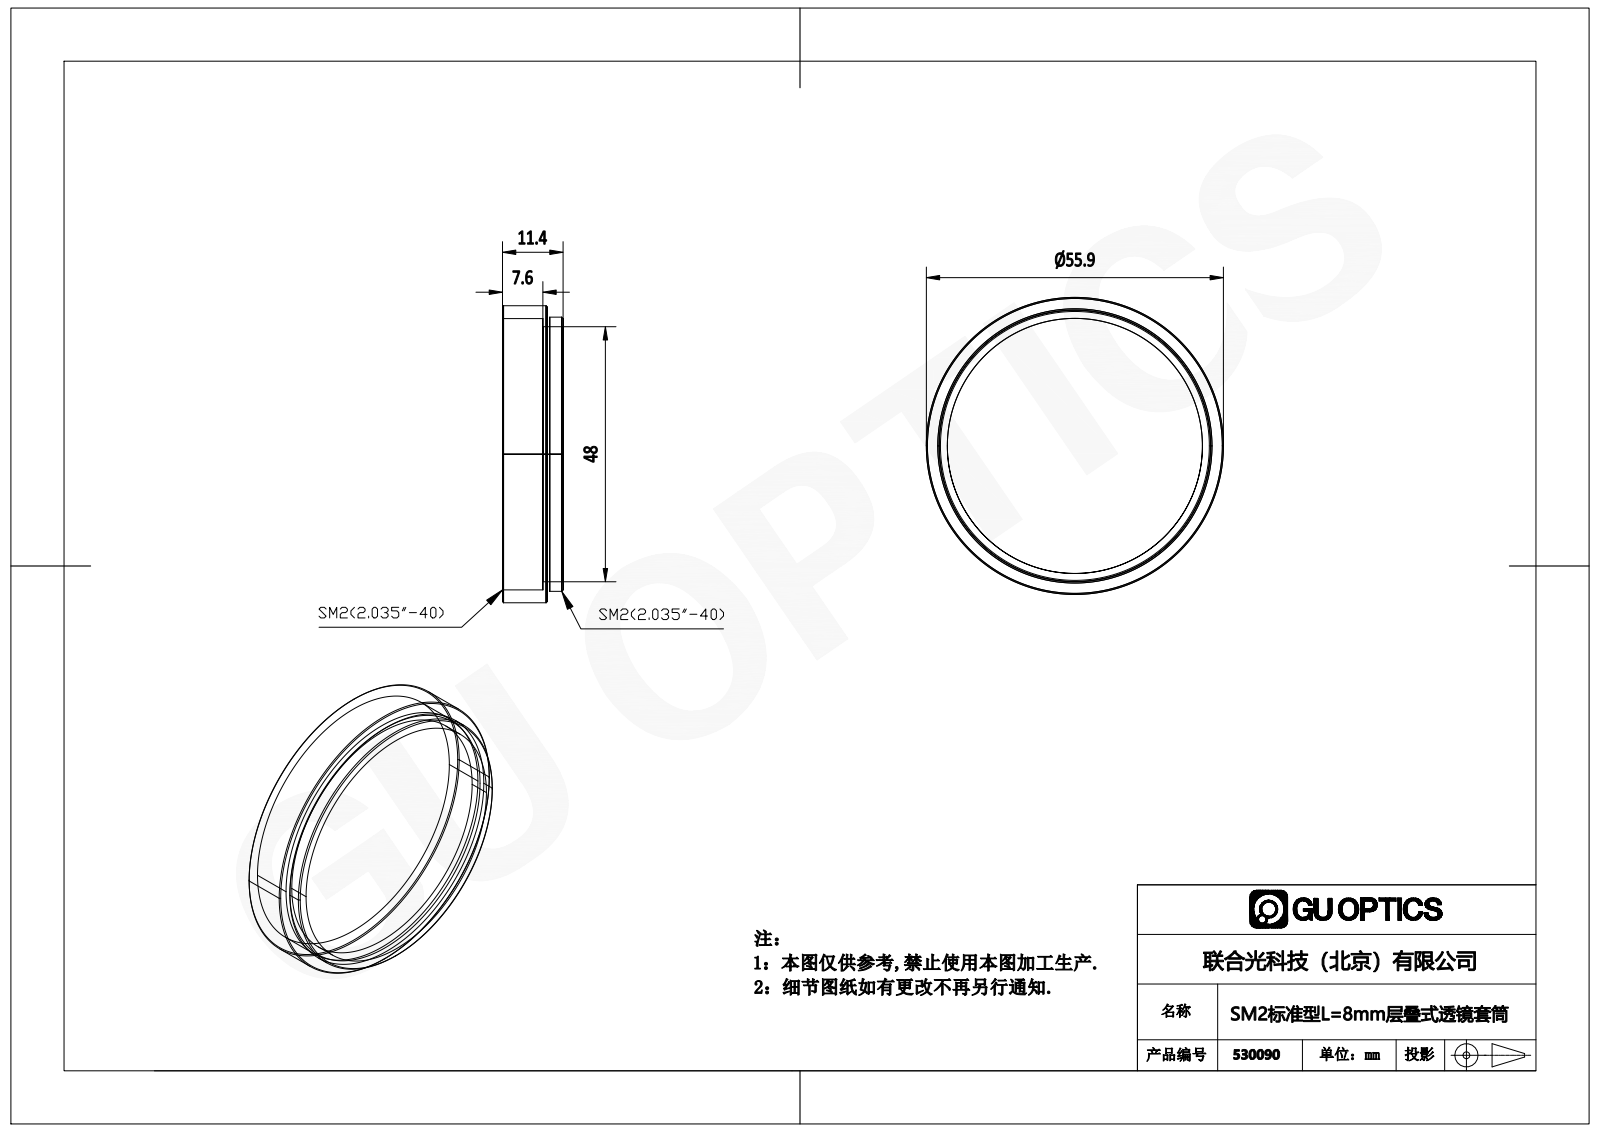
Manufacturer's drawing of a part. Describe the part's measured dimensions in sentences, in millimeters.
Its 3-D file was written by "SolidWorks 2018 (AUTOMOTIVE_DESIGN)". It is 0 solids with 36 faces: 13 planar, 12 cylindrical and 11 other. Overall it measures 55.9 by 55.9 by 11.4 millimeters. Round holes: 1 of diameter 47.69, 1 of diameter 48, 1 of diameter 51.05. Round bosses or shafts: 1 of diameter 55.9, 1 of diameter 51.6, 1 of diameter 50.6. The main face-to-face distances are 8.4, 11.4, 3, 7.6, 0.8, 3.8, 2.97, 4.63, 5.43, 8.43.
